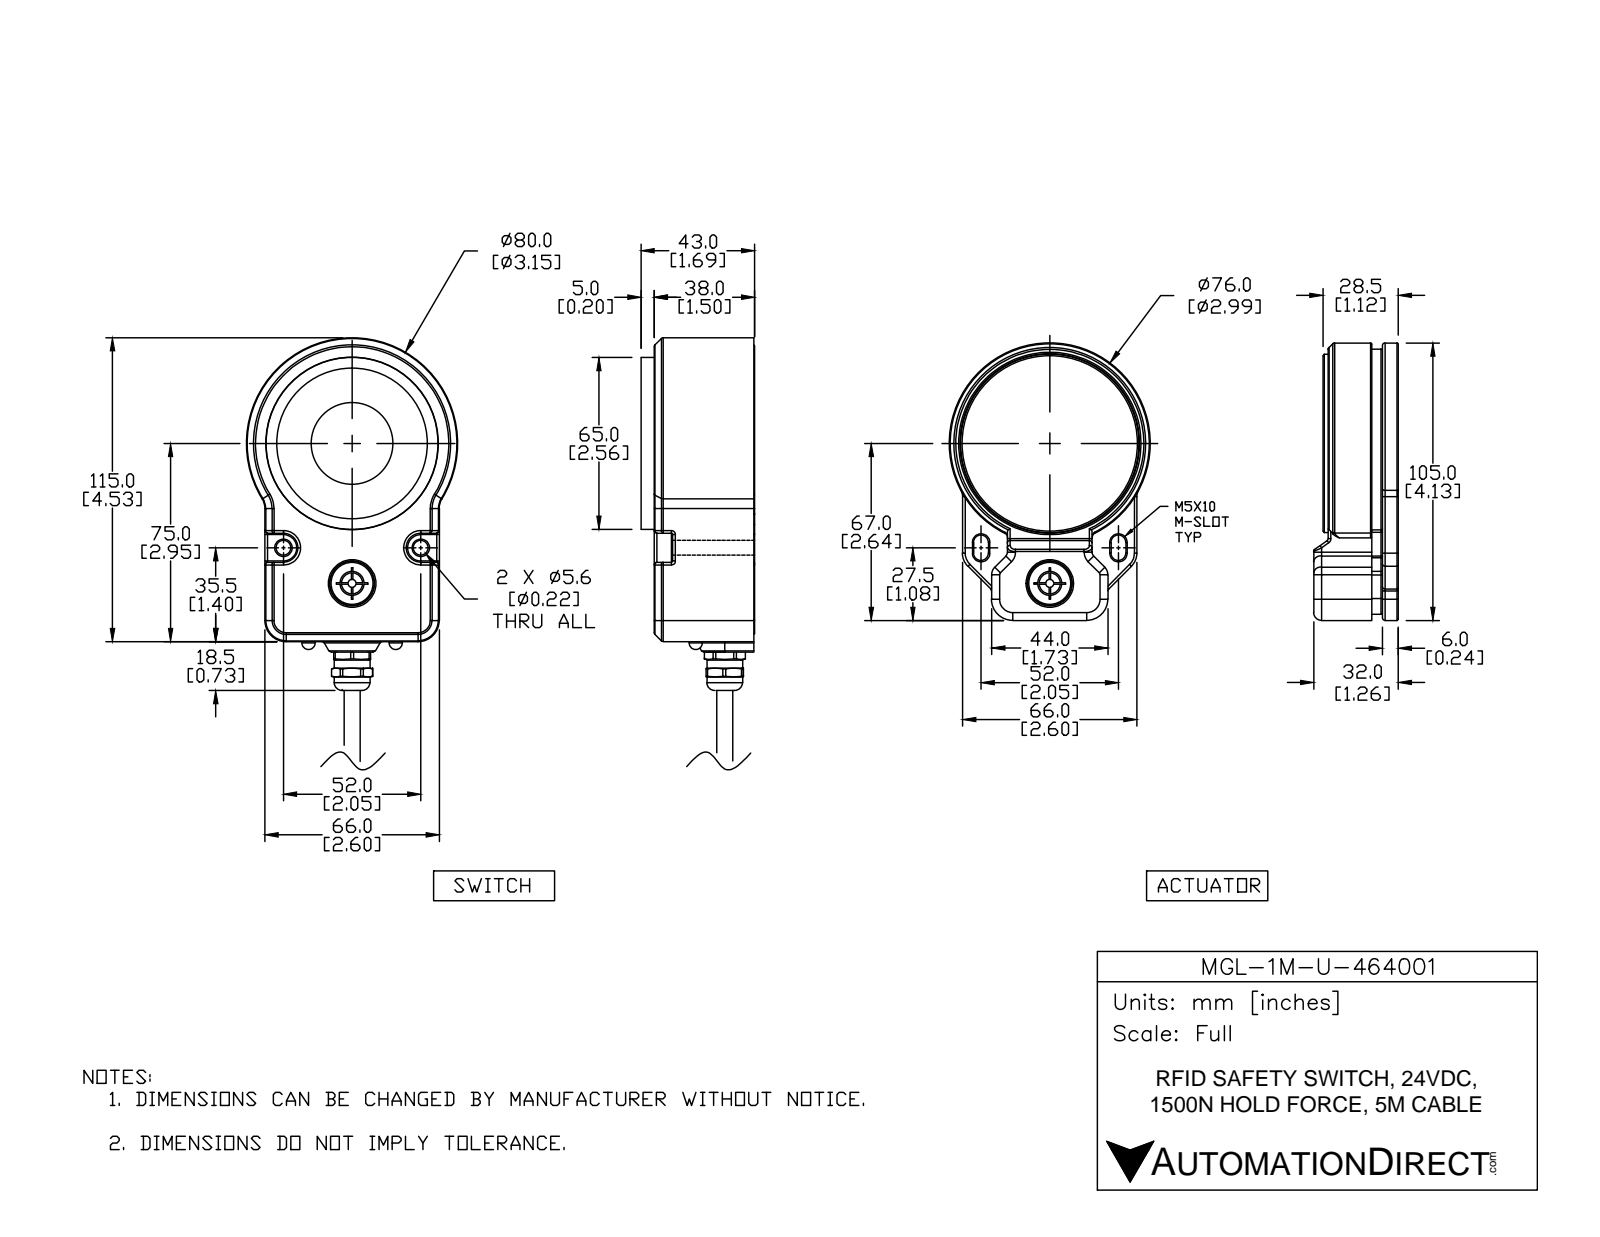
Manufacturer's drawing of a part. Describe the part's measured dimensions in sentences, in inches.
The part is named "MGL-1M-U-464001; MGL-1M-U-464001_2; MGL-1M-U-464001_1". Its 3-D file was written by "SolidWorks 2017 (AUTOMOTIVE_DESIGN)". It is 19 solids with 1753 faces: 428 planar, 743 cylindrical and 582 other. Overall it measures 8.163 by 3.15 by 2.85 inches. Its volume is 19.31 cubic inches and its surface area 219.5 square inches. Round holes: 8 of diameter 0.098, 6 of diameter 0.13, 6 of diameter 0.197, 5 of diameter 0.453, 3 of diameter 0.157, 3 of diameter 0.315, 3 of diameter 0.354, 2 of diameter 0.22, 2 of diameter 0.276, 2 of diameter 0.374, 2 of diameter 0.465, 1 of diameter 0.252. Round bosses or shafts: 4 of diameter 0.02, 3 of diameter 0.079, 2 of diameter 0.472, 2 of diameter 0.228, 2 of diameter 0.213, 2 of diameter 0.047, 1 of diameter 2.992, 1 of diameter 2.811. Partial cylindrical surfaces (rounded edges, fillets, slot ends): 186 of radius 0.02, 86 of radius 0.039, 26 of radius 0.079, 17 of radius 0.012, 13 of radius 0.118, 9 of radius 0.157, 8 of radius 0.217, 7 of radius 0.024. The main face-to-face distances are 0.315, 0.236, 2.299, 1.378, 0.118, 2.614, 0.413, 2.201, 2.85, 0.65. The hole center spacings are 1.392, 1.969, 0.984, 1.28, 1.537, 0.787, 1.364, 0.349.
